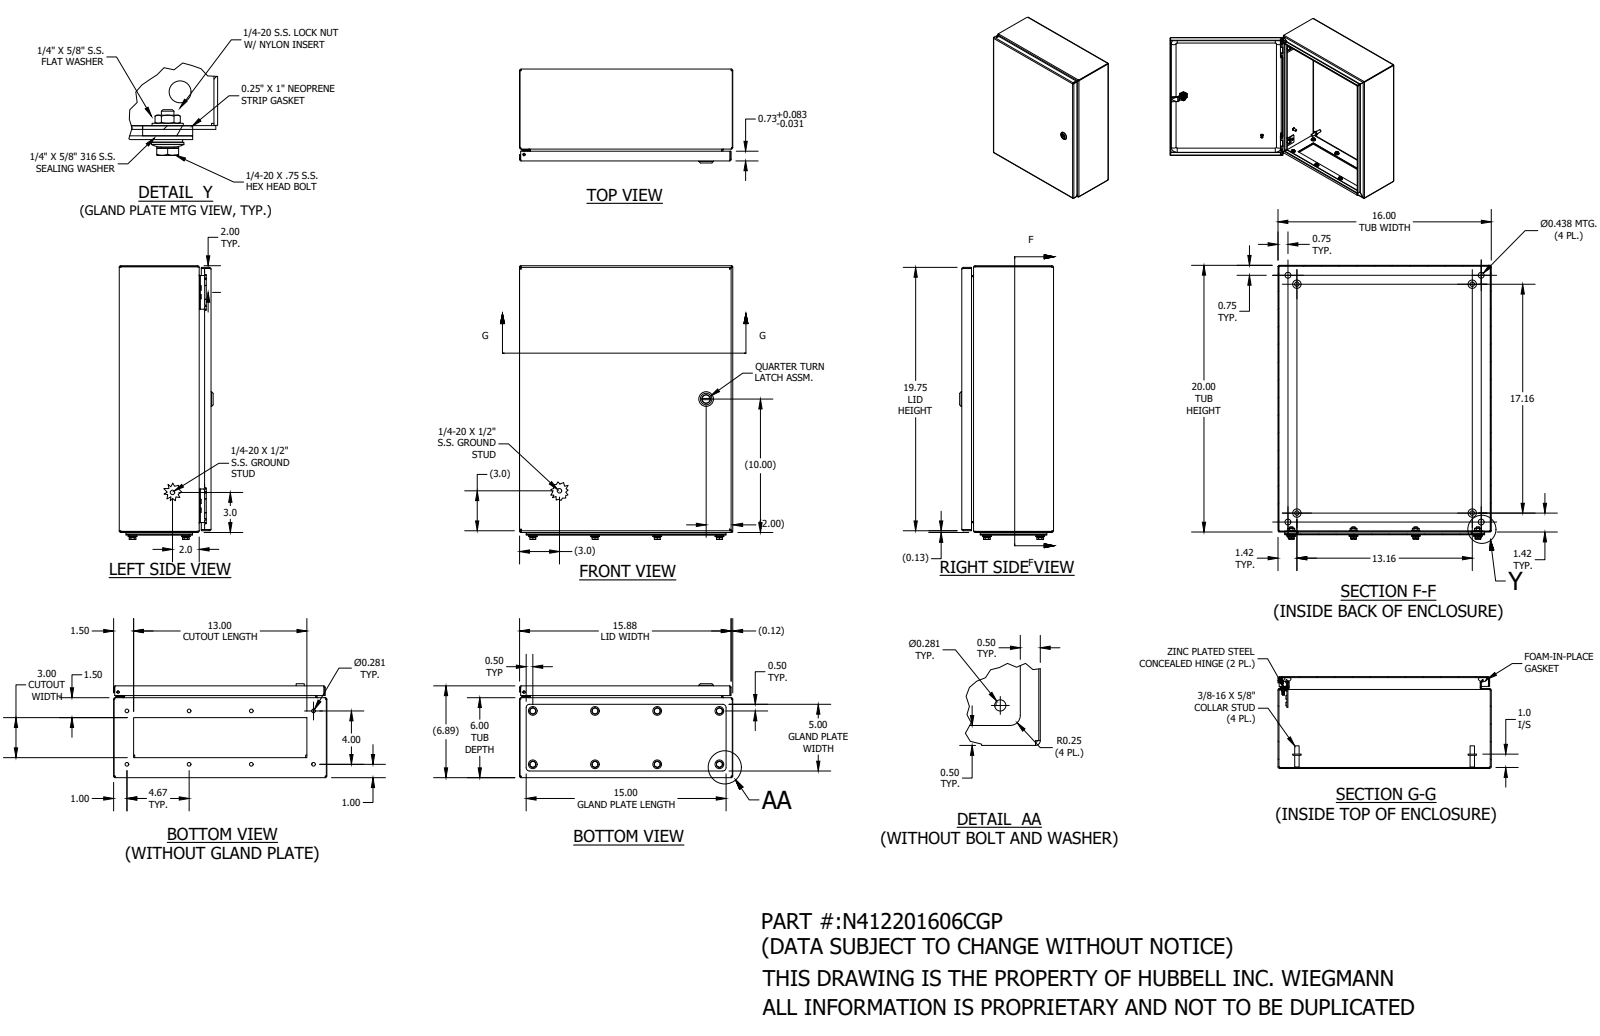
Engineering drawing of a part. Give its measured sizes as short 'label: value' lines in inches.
name: N412201606CGP
written by: SolidWorks 2021 (AUTOMOTIVE_DESIGN)
unit: in
bodies: 72 solids, 2038 faces (796 planar, 625 cylindrical, 617 other)
size: 20.519 × 16 × 7.044
volume: 112.9 in³; area: 2 763 in²
holes: 8× ⌀0.16, 8× ⌀0.211, 8× ⌀0.275, 8× ⌀0.281, 8× ⌀0.29, 7× ⌀0.235, 6× ⌀0.35, 5× ⌀0.188, 4× ⌀0.093, 4× ⌀0.167, 4× ⌀0.437, 2× ⌀0.156
bosses: 18× ⌀0.25, 10× ⌀0.625, 8× ⌀0.65, 8× ⌀0.6, 8× ⌀0.438, 4× ⌀0.36, 4× ⌀0.33, 4× ⌀0.32
rounds: 30× R0.012, 26× R0.05, 20× R0.047, 20× R0.121, 13× R0.02, 8× R0.125, 8× R0.13, 5× R0.157
face distances: 0.074, 6.812, 0.074, 6.738, 6.886, 15.926, 15.852, 16, 0.204, 20.056
hole spacings: 6.146, 4, 4.667, 16.004, 9.333, 9.333, 10.154, 0.658
